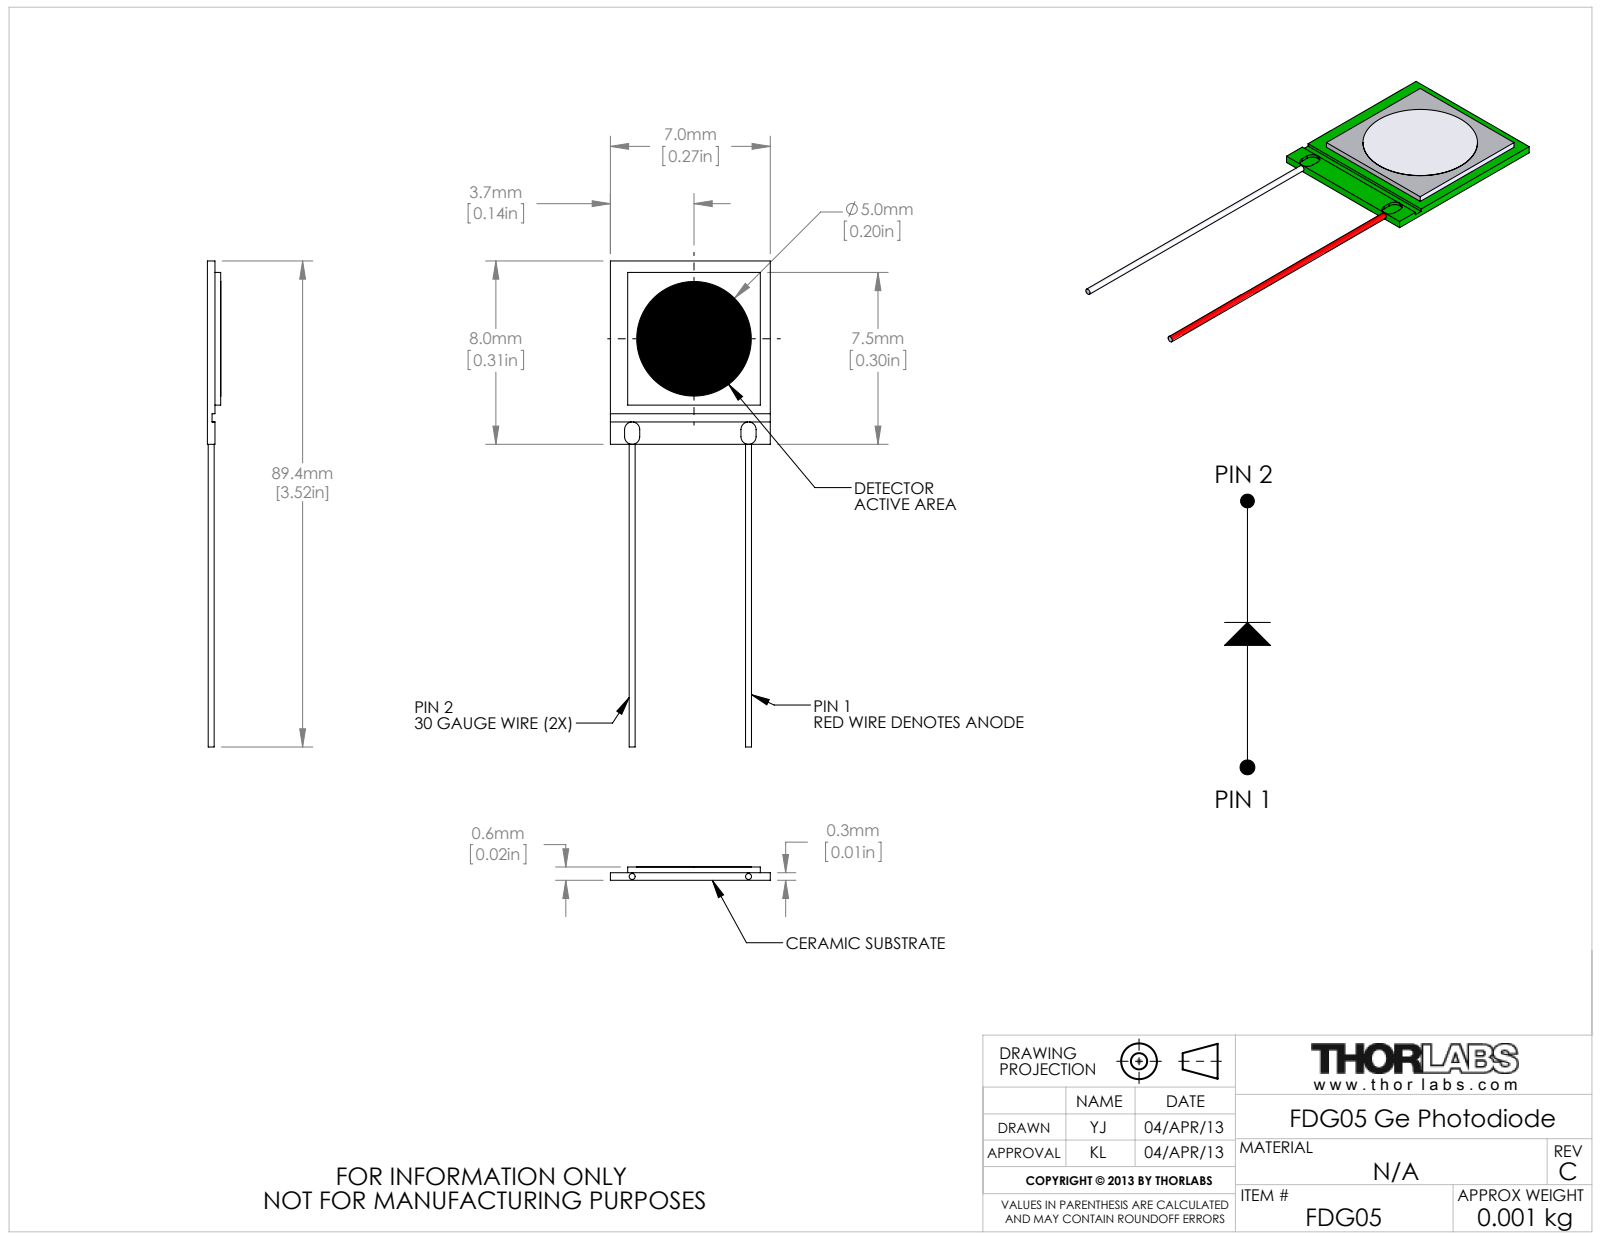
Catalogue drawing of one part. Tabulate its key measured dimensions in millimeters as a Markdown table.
| quantity | value |
| --- | --- |
| part name | 2823-E0W |
| STEP written by | SolidWorks 2012 (AUTOMOTIVE_DESIGN) |
| units | millimeters |
| bodies | 3 solids, 46 faces (30 planar, 16 cylindrical, 0 other) |
| overall size | 21.21 × 6.98 × 0.58 |
| volume | 28 mm³ |
| surface area | 151 mm² |
| round bosses / shafts (diameter × count) | 0.26 × 2, 5 × 1 |
| partial cylindrical surfaces (radius × count) | 0.33 × 4 |
| main face-to-face distances | 0.59, 0.33, 0.58, 0.38, 0.39, 5.79, 6.98, 8, 6.29, 1.71 |
